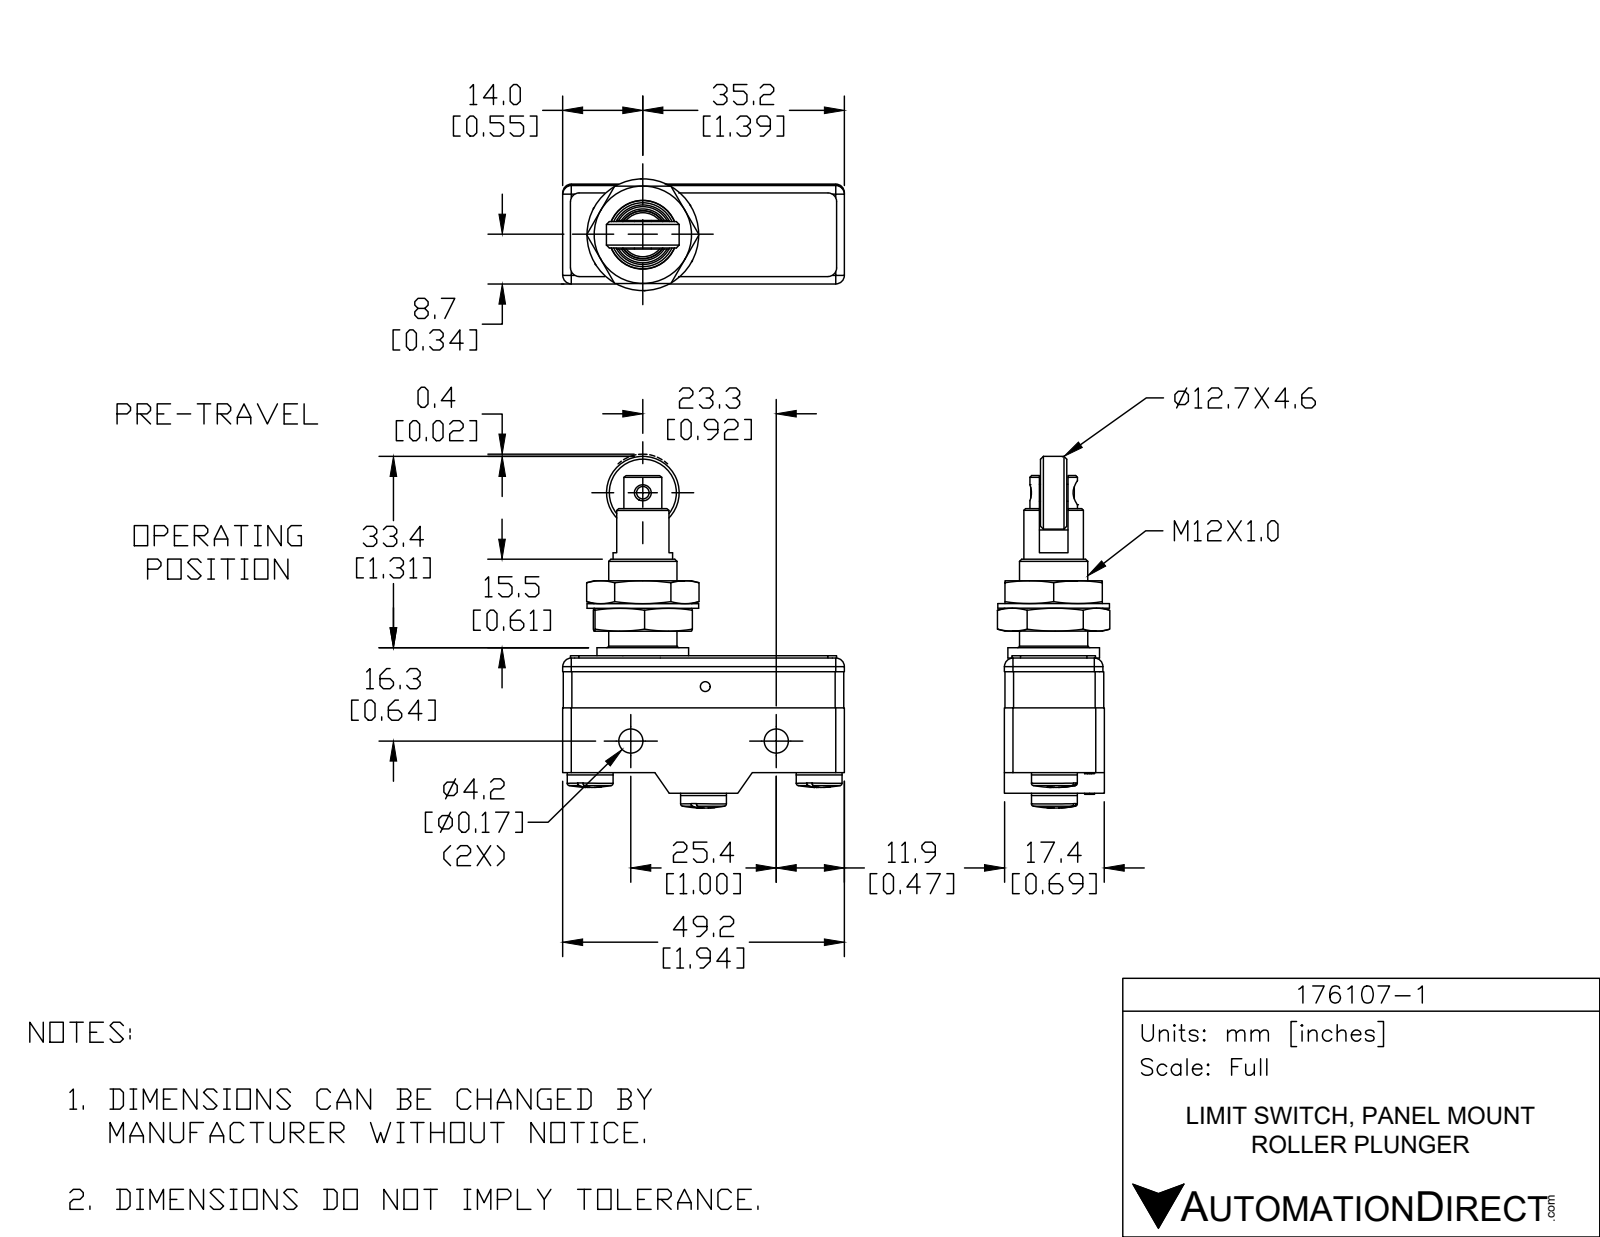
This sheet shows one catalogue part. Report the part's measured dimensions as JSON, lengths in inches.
{"part_name": "176-MS (Screw Terminal)-Panel Mount Roller Plunger", "step_written_by": "SolidWorks 2018 (AUTOMOTIVE_DESIGN)", "units": "inches", "bodies": {"solids": 15, "faces": 605, "planar": 263, "cylindrical": 144, "other": 198}, "overall_size": [2.442, 1.937, 0.772], "volume_in3": 1.368, "surface_area_in2": 19.81, "round_holes": [[0.15, 3], [0.236, 3], [0.165, 2], [0.067, 1], [0.079, 1], [0.126, 1], [0.161, 1], [0.295, 1], [0.331, 1], [0.43, 1]], "round_bosses_or_shafts": [[0.315, 3], [0.768, 1], [0.63, 1], [0.626, 1], [0.5, 1], [0.47, 1], [0.409, 1], [0.327, 1]], "partial_cylinders_radius": [[0.059, 18], [0.012, 12], [0.116, 3], [0.25, 1], [0.317, 1]], "face_to_face_distances": [0.693, 0.803, 0.683, 0.687, 0.016, 0.11, 0.189, 1.142, 0.031, 0.157], "hole_center_spacings": [0.354, 0.425, 0.615, 0.634, 0.78, 0.795, 1, 1.22]}
